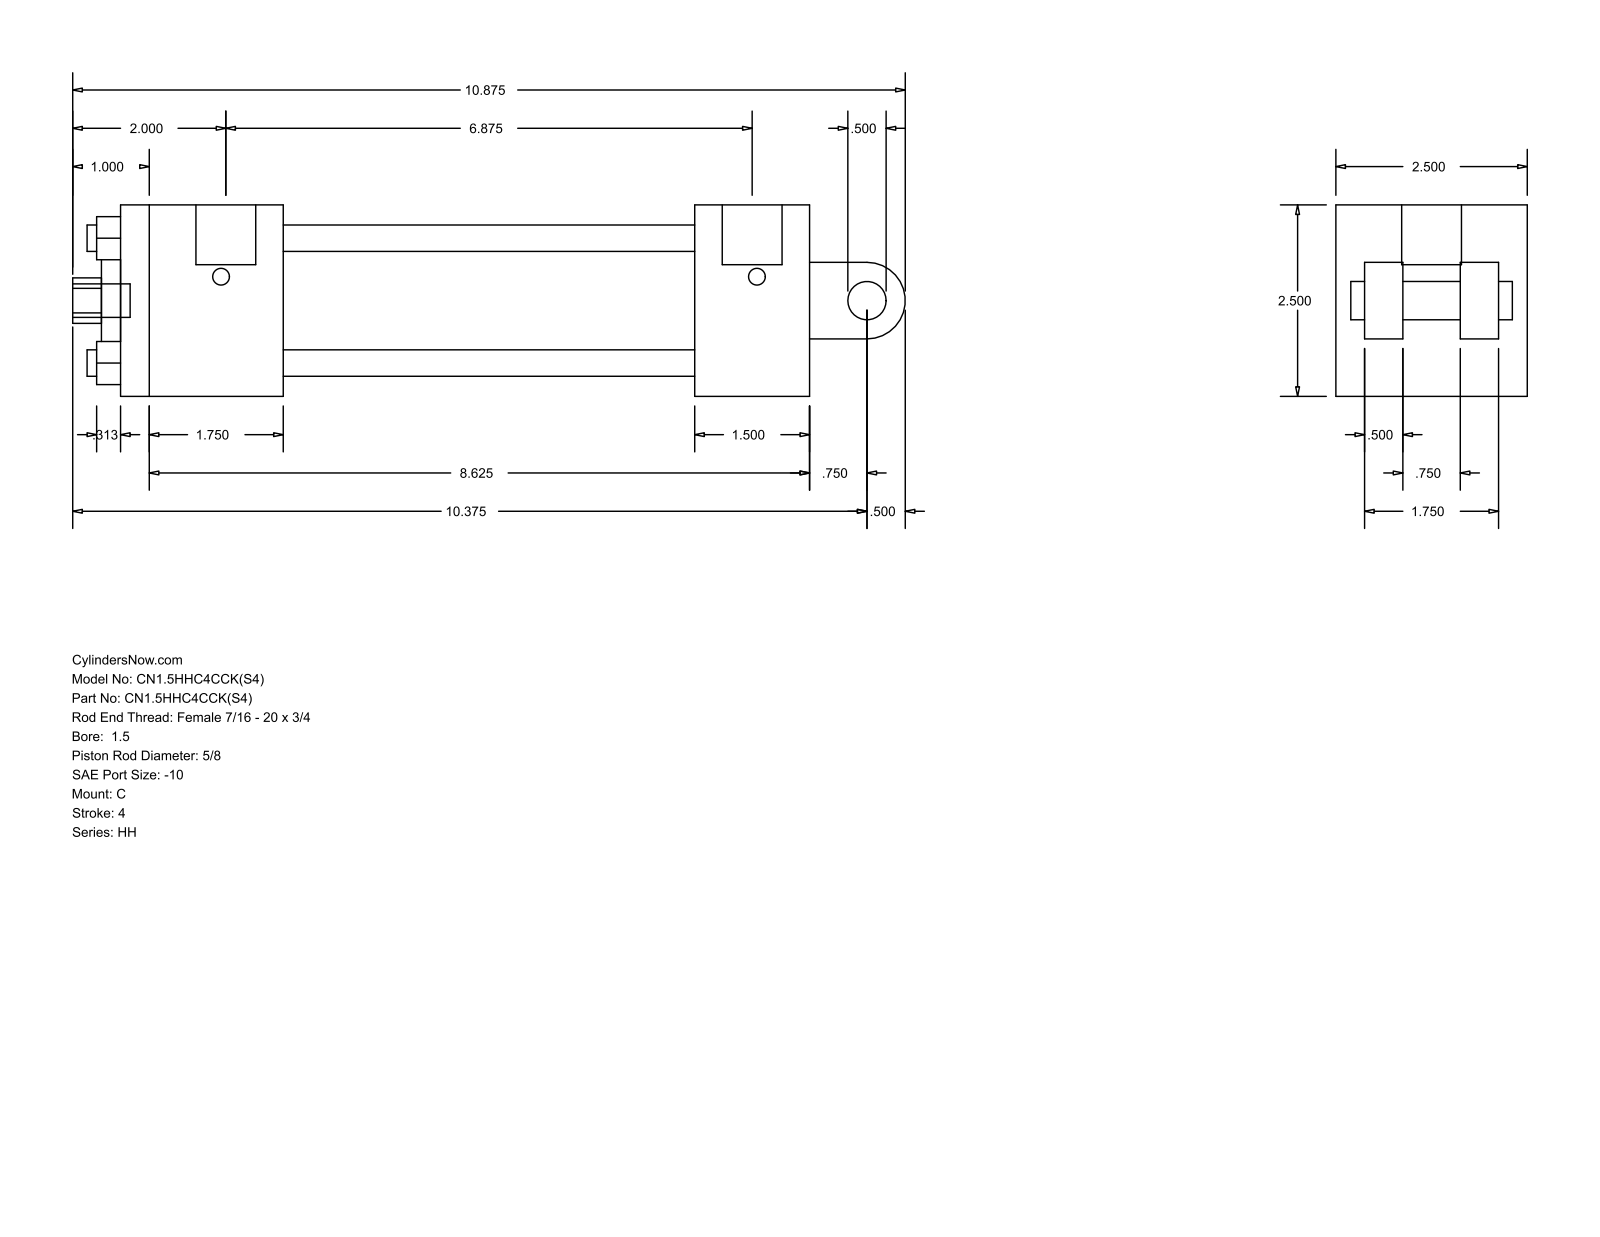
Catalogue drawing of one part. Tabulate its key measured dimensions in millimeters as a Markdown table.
| quantity | value |
| --- | --- |
| part name | HH_C__0150_0.625 |
| STEP written by | GSSL Pune (CONFIG_CONTROL_DESIGN) |
| units | millimeters |
| bodies | 0 solids, 99 faces (70 planar, 29 cylindrical, 0 other) |
| overall size | 276.23 × 63.5 × 63.5 |
| round holes (diameter × count) | 8.76 × 4, 5.56 × 2, 15.88 × 1, 19.84 × 1, 28.57 × 1, 44.45 × 1 |
| round bosses / shafts (diameter × count) | 5.56 × 2, 19.84 × 1, 12.7 × 1, 11.11 × 1 |
| partial cylindrical surfaces (radius × count) | 7.54 × 1, 12.7 × 1 |
| main face-to-face distances | 63.5, 228.59, 53.97, 190.5, 136.53, 174.62, 38.09, 12.7, 9.52, 19.05 |
| hole center spacings | 29.27, 41.4, 58.55, 1.58 |
